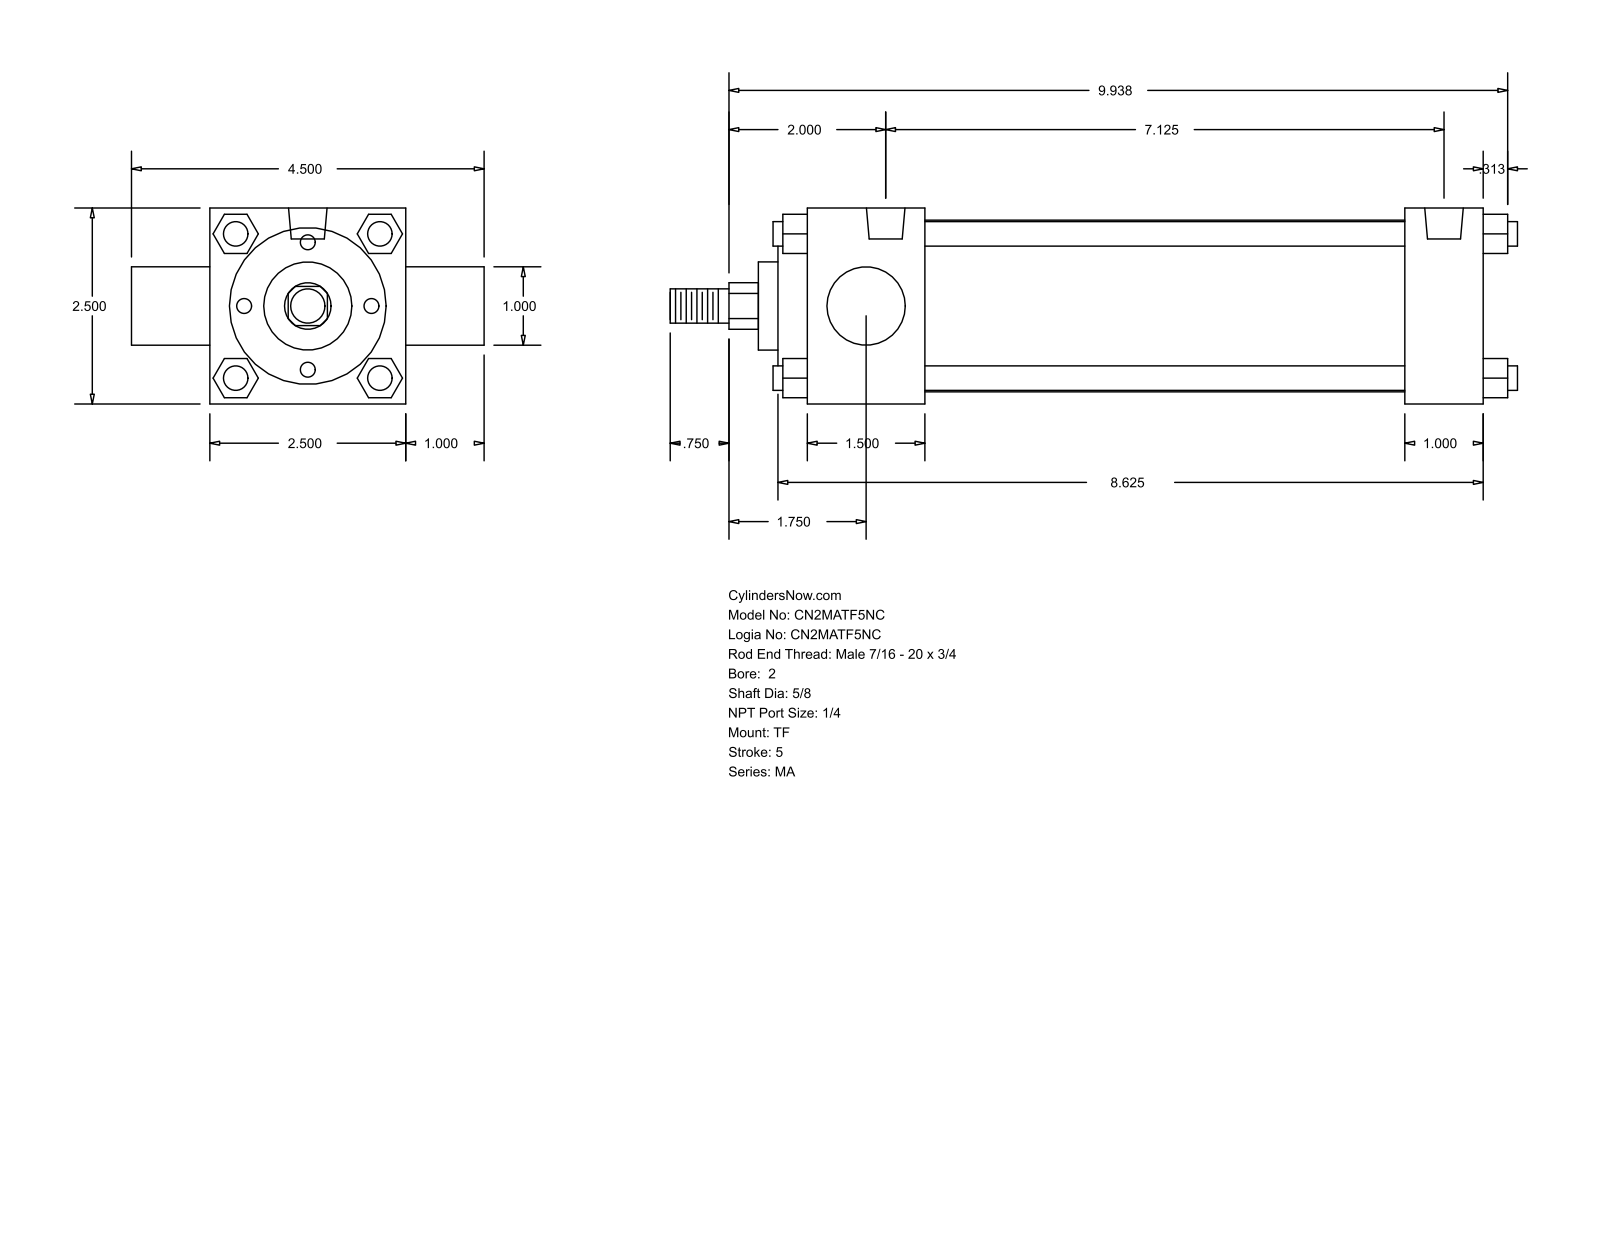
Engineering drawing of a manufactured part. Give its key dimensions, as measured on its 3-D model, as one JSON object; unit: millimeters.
{"part_name": "MA_TF__0200_0.625", "step_written_by": "GSSL Pune (CONFIG_CONTROL_DESIGN)", "units": "millimeters", "bodies": {"solids": 0, "faces": 122, "planar": 93, "cylindrical": 29, "other": 0}, "overall_size": [274.64, 114.3, 63.5], "round_holes": [[7.94, 3], [12.49, 2]], "round_bosses_or_shafts": [[7.94, 4], [55.63, 1], [50.8, 1], [28.57, 1], [25.4, 1], [15.88, 1], [11.11, 1]], "partial_cylinders_radius": [[7.54, 1]], "face_to_face_distances": [63.5, 25.4, 38.1, 219.07, 12.7, 193.67, 155.57, 180.97, 9.52, 47.62], "hole_center_spacings": [180.98]}
